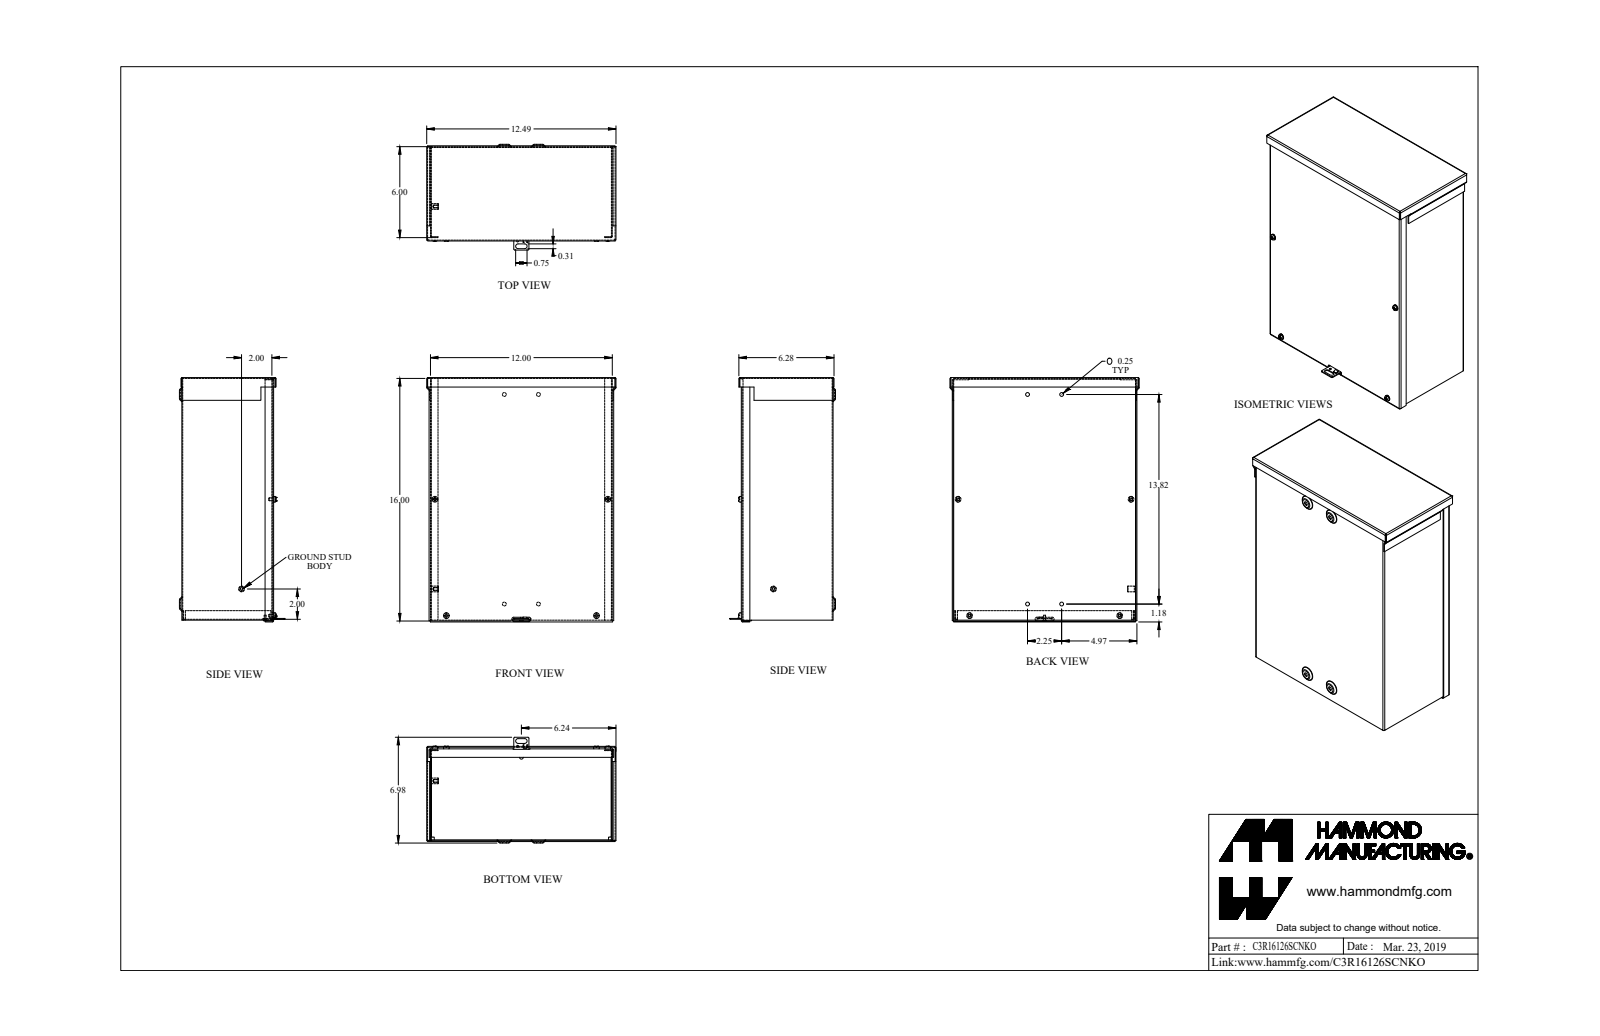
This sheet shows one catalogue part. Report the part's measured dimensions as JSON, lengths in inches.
{"part_name": "C3R16126SCNKO_Default", "step_written_by": "SolidWorks 2019 (CONFIG_CONTROL_DESIGN)", "units": "inches", "bodies": {"solids": 11, "faces": 404, "planar": 211, "cylindrical": 107, "other": 86}, "overall_size": [16.12, 12.489, 6.977], "volume_in3": 46.36, "surface_area_in2": 1639, "round_holes": [[0.17, 4], [0.25, 4], [0.125, 1], [0.137, 1], [0.156, 1]], "round_bosses_or_shafts": [[0.19, 4], [0.375, 3], [0.375, 2], [0.125, 1]], "partial_cylinders_radius": [[0.029, 21], [0.086, 21], [0.109, 8], [0.125, 8], [0.156, 2]], "face_to_face_distances": [0.057, 6, 5.943, 6.057, 11.943, 0.057, 12, 11.886, 15.886, 15.943], "hole_center_spacings": [8.291, 9.717, 2.25, 3.905, 6.127, 7.715, 13.138, 13.818]}
